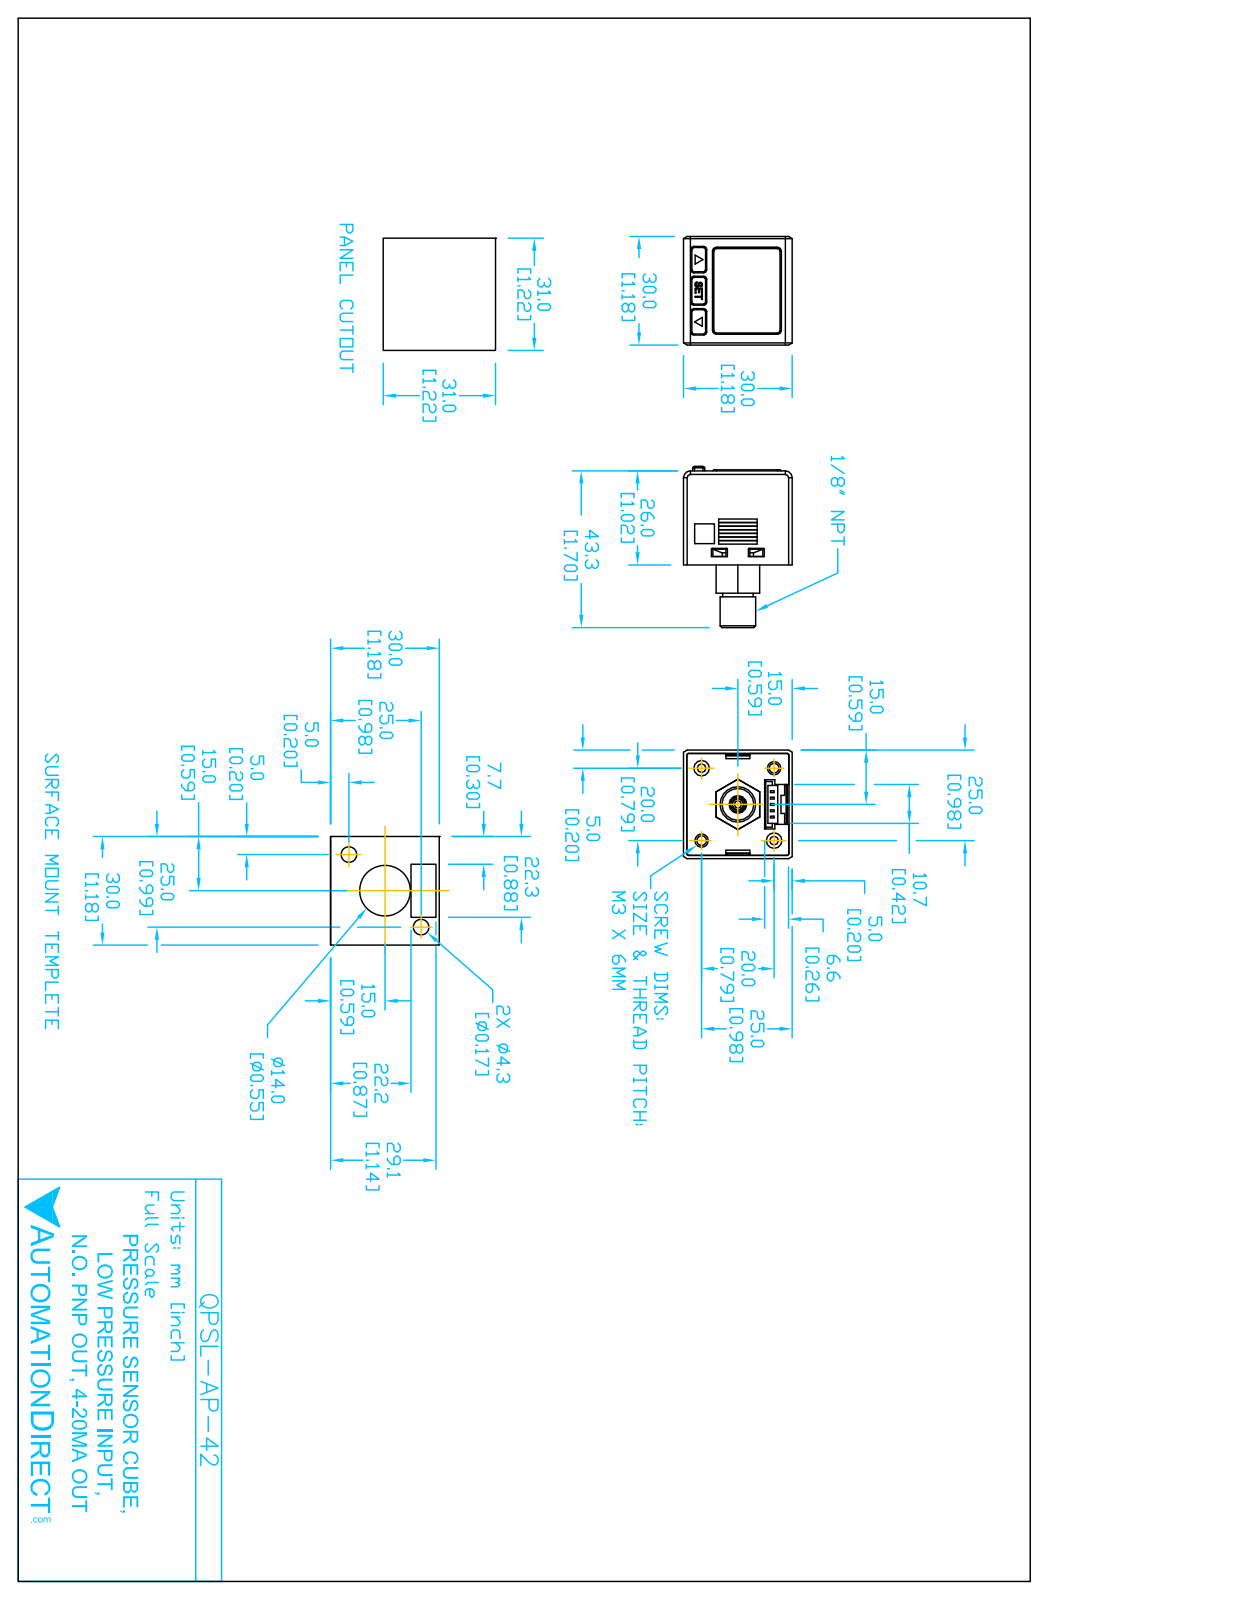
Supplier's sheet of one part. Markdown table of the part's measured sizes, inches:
| quantity | value |
| --- | --- |
| part name | QPSL-AN-42 |
| STEP written by | SolidWorks 2014 (AUTOMOTIVE_DESIGN) |
| units | inches |
| bodies | 1 solid, 386 faces (296 planar, 62 cylindrical, 28 other) |
| overall size | 1.806 × 1.18 × 1.18 |
| volume | 1.496 in³ |
| surface area | 10.41 in² |
| round holes (diameter × count) | 0.105 × 2, 0.12 × 2, 0.19 × 2, 0.165 × 1 |
| round bosses / shafts (diameter × count) | 0.375 × 1, 0.32 × 1 |
| partial cylindrical surfaces (radius × count) | 0.02 × 16, 0.015 × 8, 0.06 × 2 |
| main face-to-face distances | 1.18, 1.041, 1.04, 0.03, 0.04, 0.476, 0.052, 0.564, 0.061, 0.352 |
| hole center spacings | 0.552, 0.78, 1.104 |
